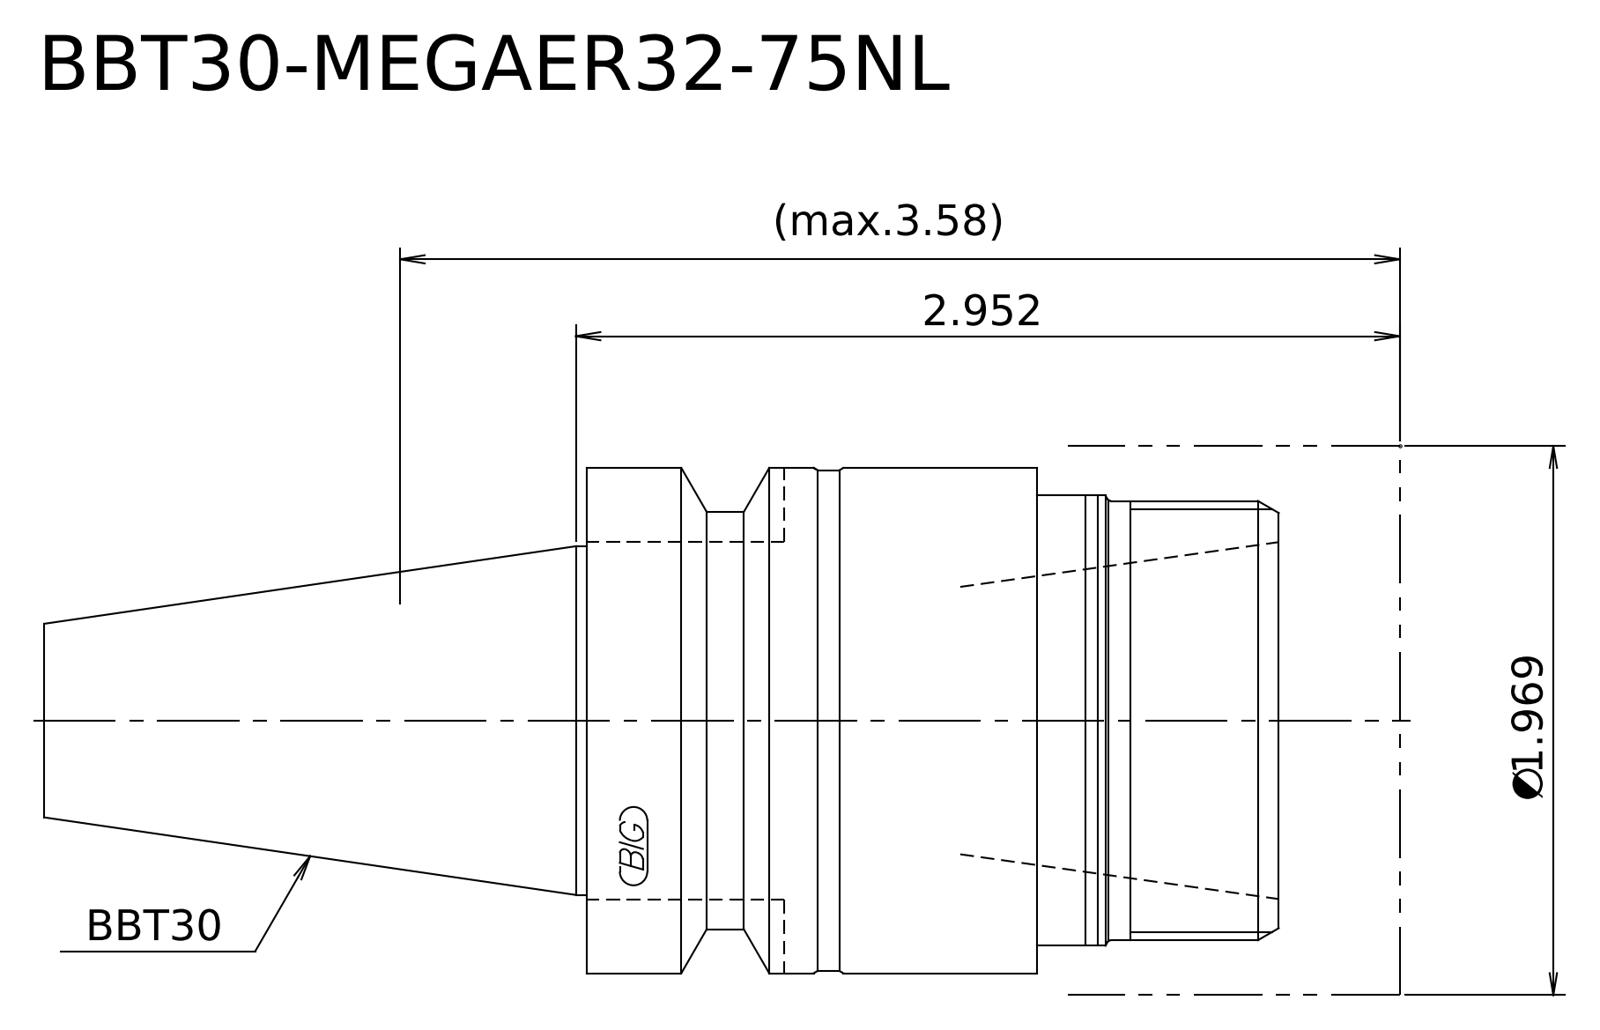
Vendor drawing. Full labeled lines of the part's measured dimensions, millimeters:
STEP written by: Kubotek KeyCreator 2011 V10.0.2 (22737) (automotive_design)
Units: millimetres
Bodies: 2 solids, 18 faces (6 planar, 7 cylindrical, 5 other)
Overall size (bounding box): 123.4 × 50 × 50
Volume: 176 913 mm³ · Surface area: 24 385 mm²
Round bosses / shafts (diameter × count): ⌀50 ×1, ⌀46 ×1, ⌀41 ×1, ⌀40 ×1, ⌀38 ×1, ⌀31.75 ×1
Main face-to-face distances: 30.2, 11, 19.2, 74, 63, 43.8, 33, 22, 2.8, 41
